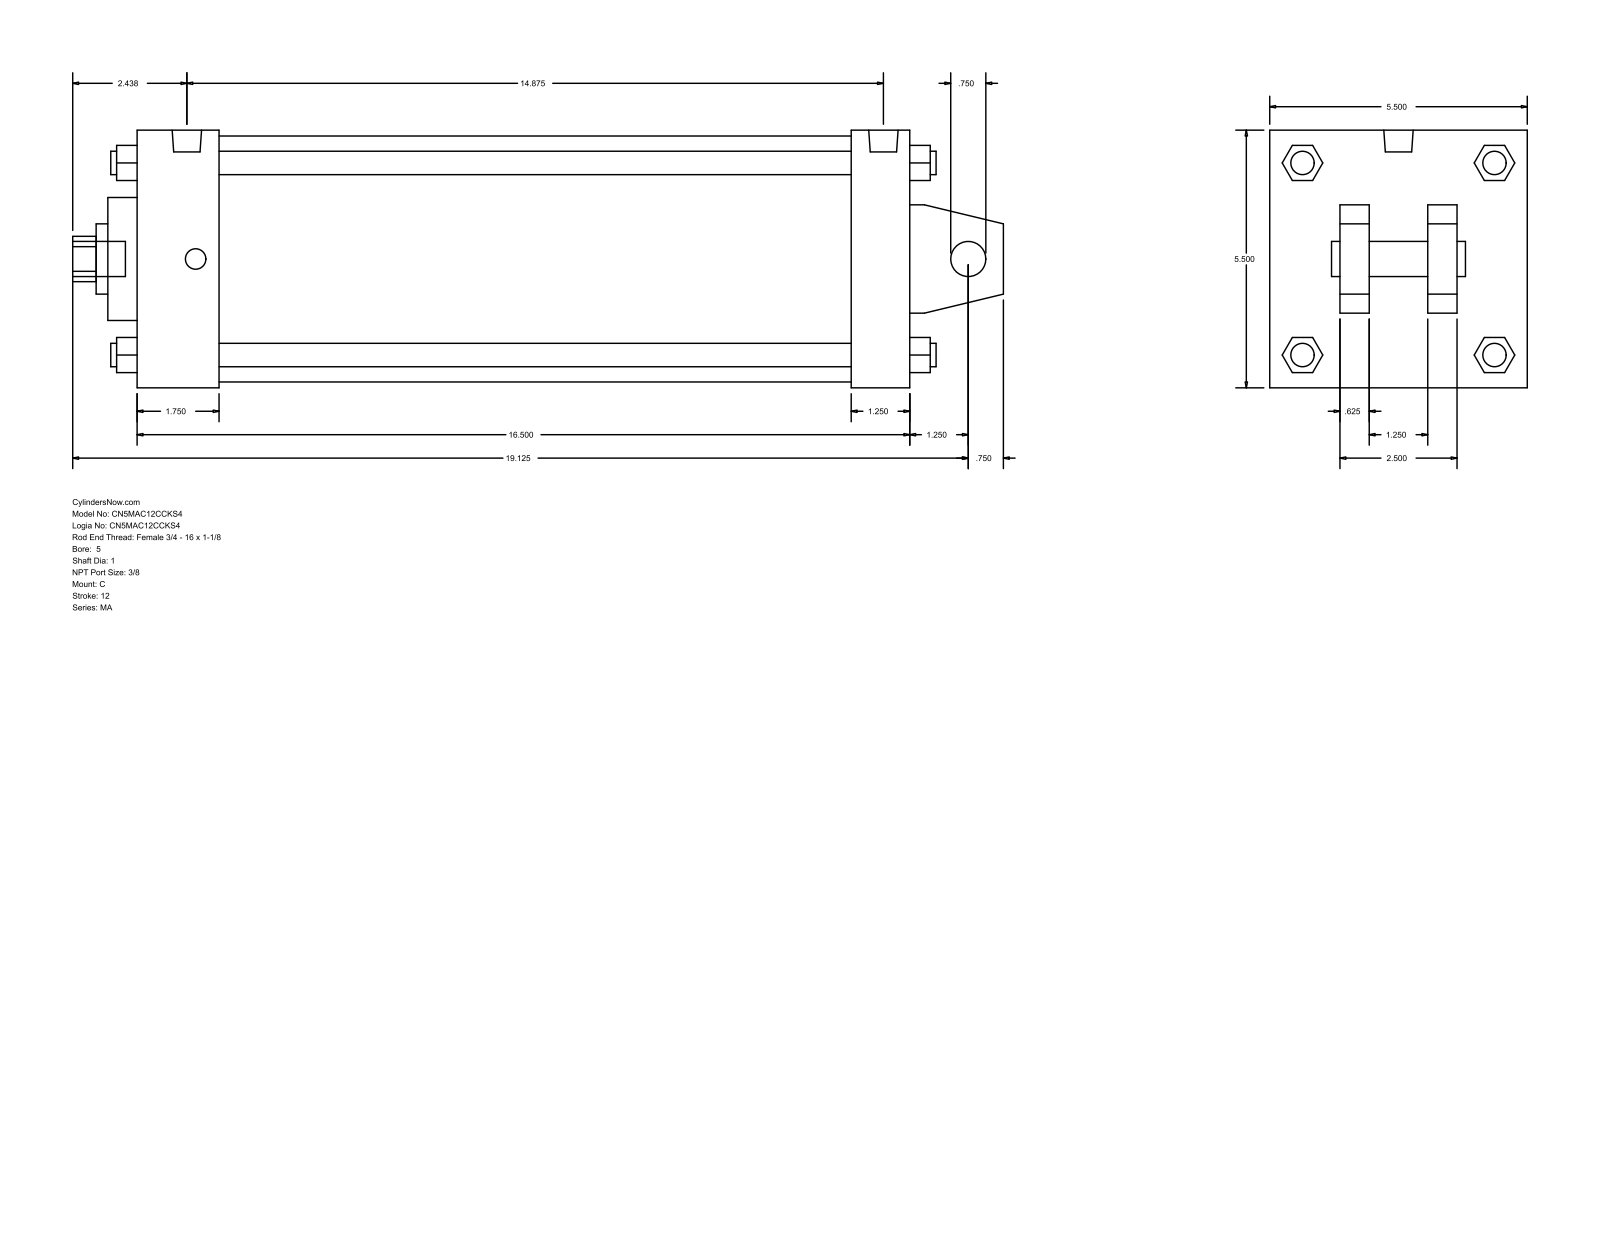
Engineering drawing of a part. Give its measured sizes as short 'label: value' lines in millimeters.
name: MA_C__0500_1
written by: GSSL Pune (CONFIG_CONTROL_DESIGN)
unit: mm
bodies: 0 solids, 141 faces (109 planar, 32 cylindrical, 0 other)
size: 504.82 × 139.7 × 139.7
holes: 1× ⌀19.05, 1× ⌀25.4, 1× ⌀38.1, 1× ⌀66.67, 1× ⌀133.35
bosses: 4× ⌀12.7, 4× ⌀11.11, 2× ⌀15.93, 1× ⌀19.05
rounds: 1× R12.29
face distances: 139.7, 419.1, 15.87, 387.35, 31.75, 44.46, 342.89, 374.64, 38.1, 101.6
